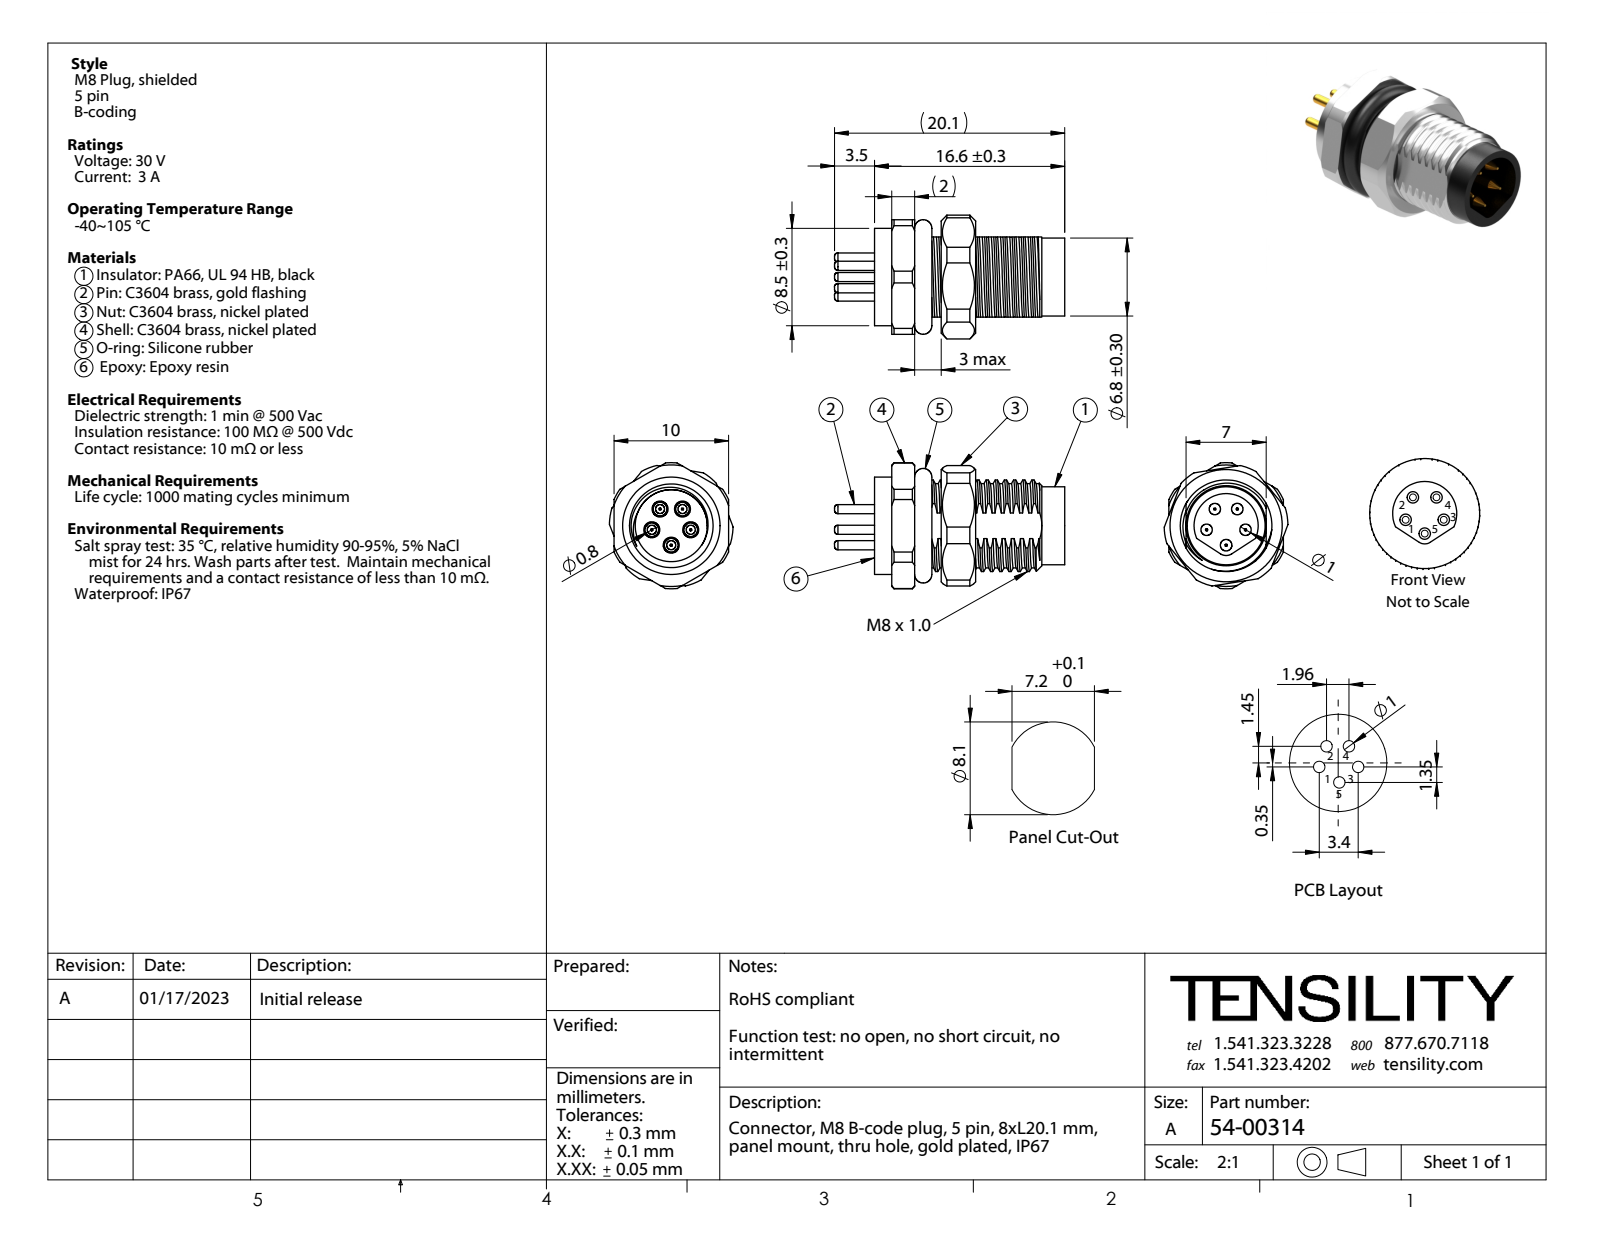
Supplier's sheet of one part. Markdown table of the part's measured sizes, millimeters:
| quantity | value |
| --- | --- |
| part name | 54-00314-06; 54-00314-01; 54-00314-04; 54-00314-03 (+2 more) |
| STEP written by | SolidWorks 2021 (CONFIG_CONTROL_DESIGN) |
| units | millimeters |
| bodies | 9 solids, 375 faces (64 planar, 163 cylindrical, 148 other) |
| overall size | 20.1 × 11 × 10.8 |
| volume | 867 mm³ |
| surface area | 2 328 mm² |
| round holes (diameter × count) | 1 × 5, 6.3 × 1, 7 × 1 |
| round bosses / shafts (diameter × count) | 1.4 × 5, 0.8 × 5, 8.5 × 1, 7.35 × 1, 6.8 × 1 |
| partial cylindrical surfaces (radius × count) | 0.9 × 1, 2.8 × 1, 4 × 1, 5.4 × 1, 5.5 × 1 |
| main face-to-face distances | 10, 2, 1.5, 3, 4.32, 7, 13.1, 7.32, 5.32, 2.32 |
| hole center spacings | 1.74, 1.75, 1.94, 2.17, 3.23, 3.3, 1.7, 1.96 |
